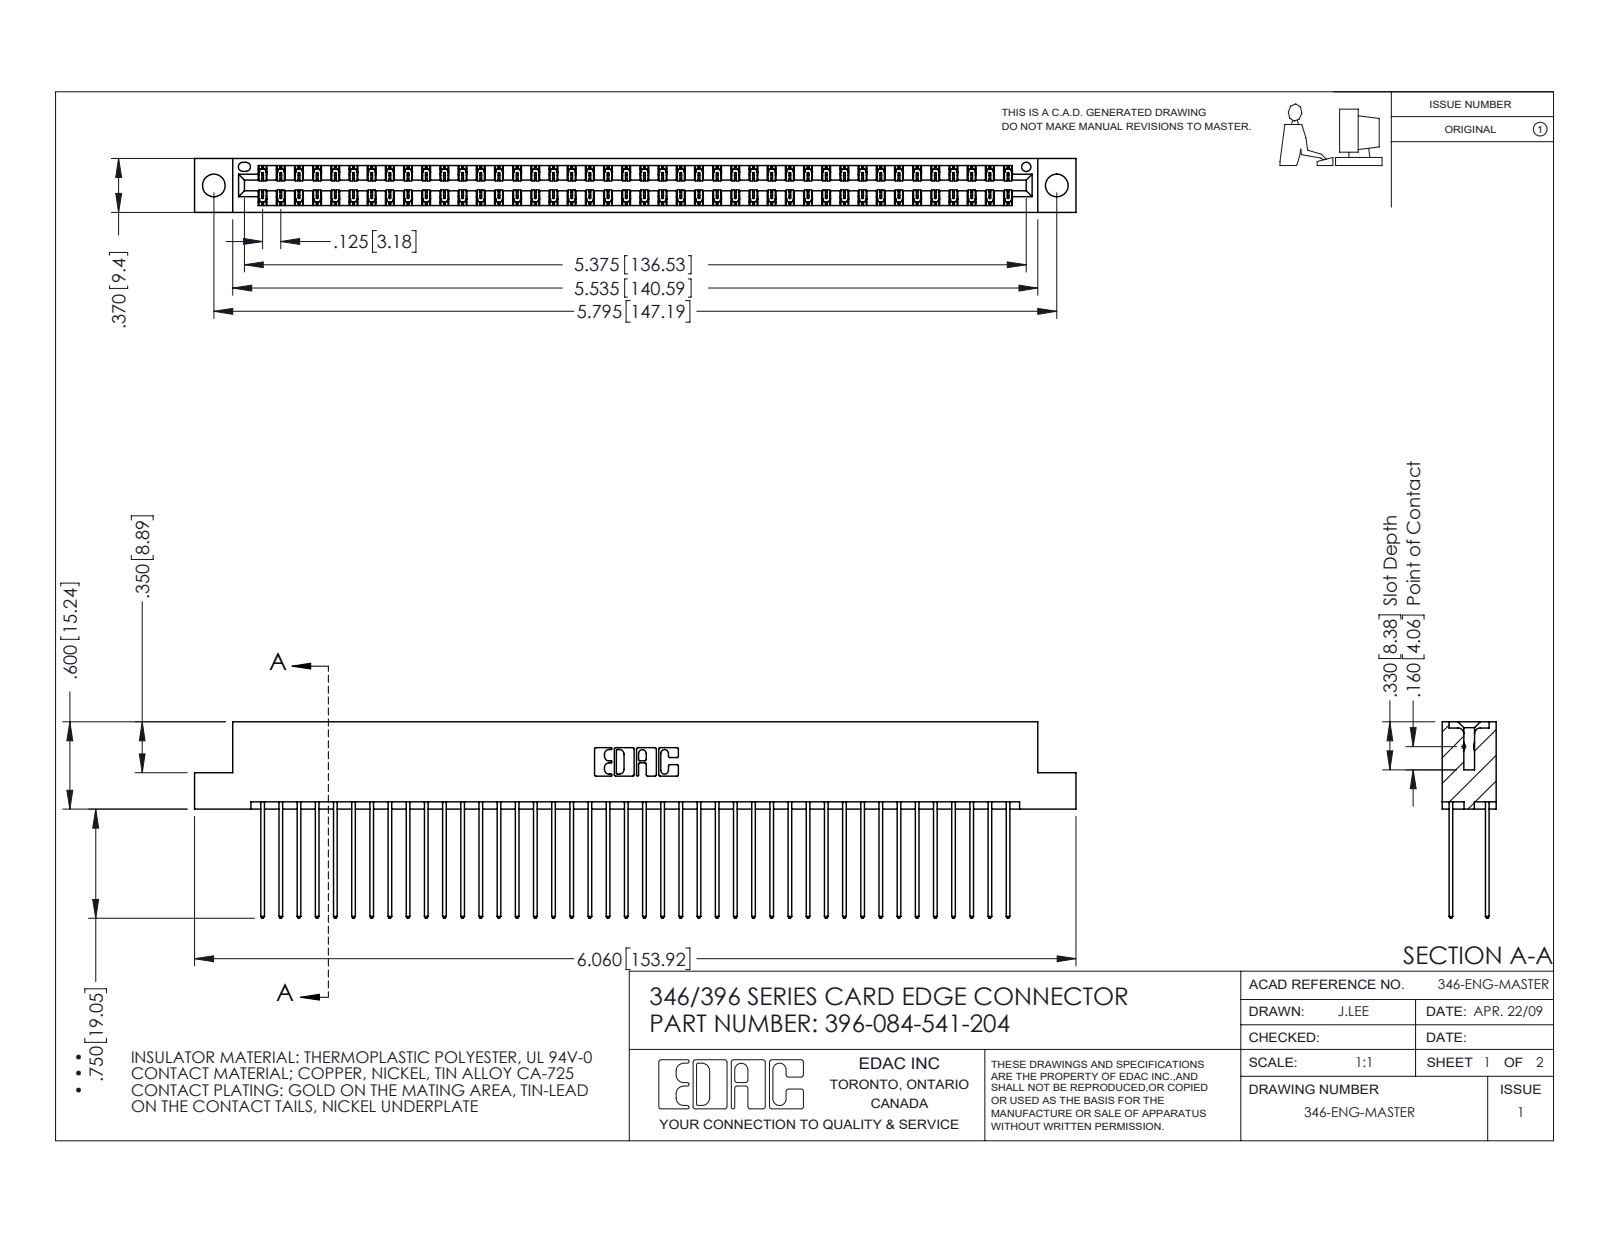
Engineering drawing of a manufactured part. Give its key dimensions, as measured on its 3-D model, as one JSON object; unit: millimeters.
{"part_name": "396-084-541-204; 346 Part_Flush Mounting Lugs - 0.156 Dia-TH; 345-292-001_345-293-141", "step_written_by": "SolidWorks 2016 (CONFIG_CONTROL_DESIGN)", "units": "millimeters", "bodies": {"solids": 85, "faces": 4490, "planar": 3016, "cylindrical": 1474, "other": 0}, "overall_size": [153.9, 34.3, 9.4], "volume_mm3": 15400, "surface_area_mm2": 23300, "round_holes": [[4, 2], [1.6, 1]], "partial_cylinders_radius": [[0.2, 126], [0.3, 84], [0.3, 22], [0.2, 6], [0.8, 6], [0.7, 3], [0.4, 2], [0.6, 2]], "face_to_face_distances": [1.2, 8.2, 6.4, 1.8, 7.6, 0.6, 9.4, 7, 5.7, 3.8], "hole_center_spacings": [6.2, 141.9, 147.2]}
